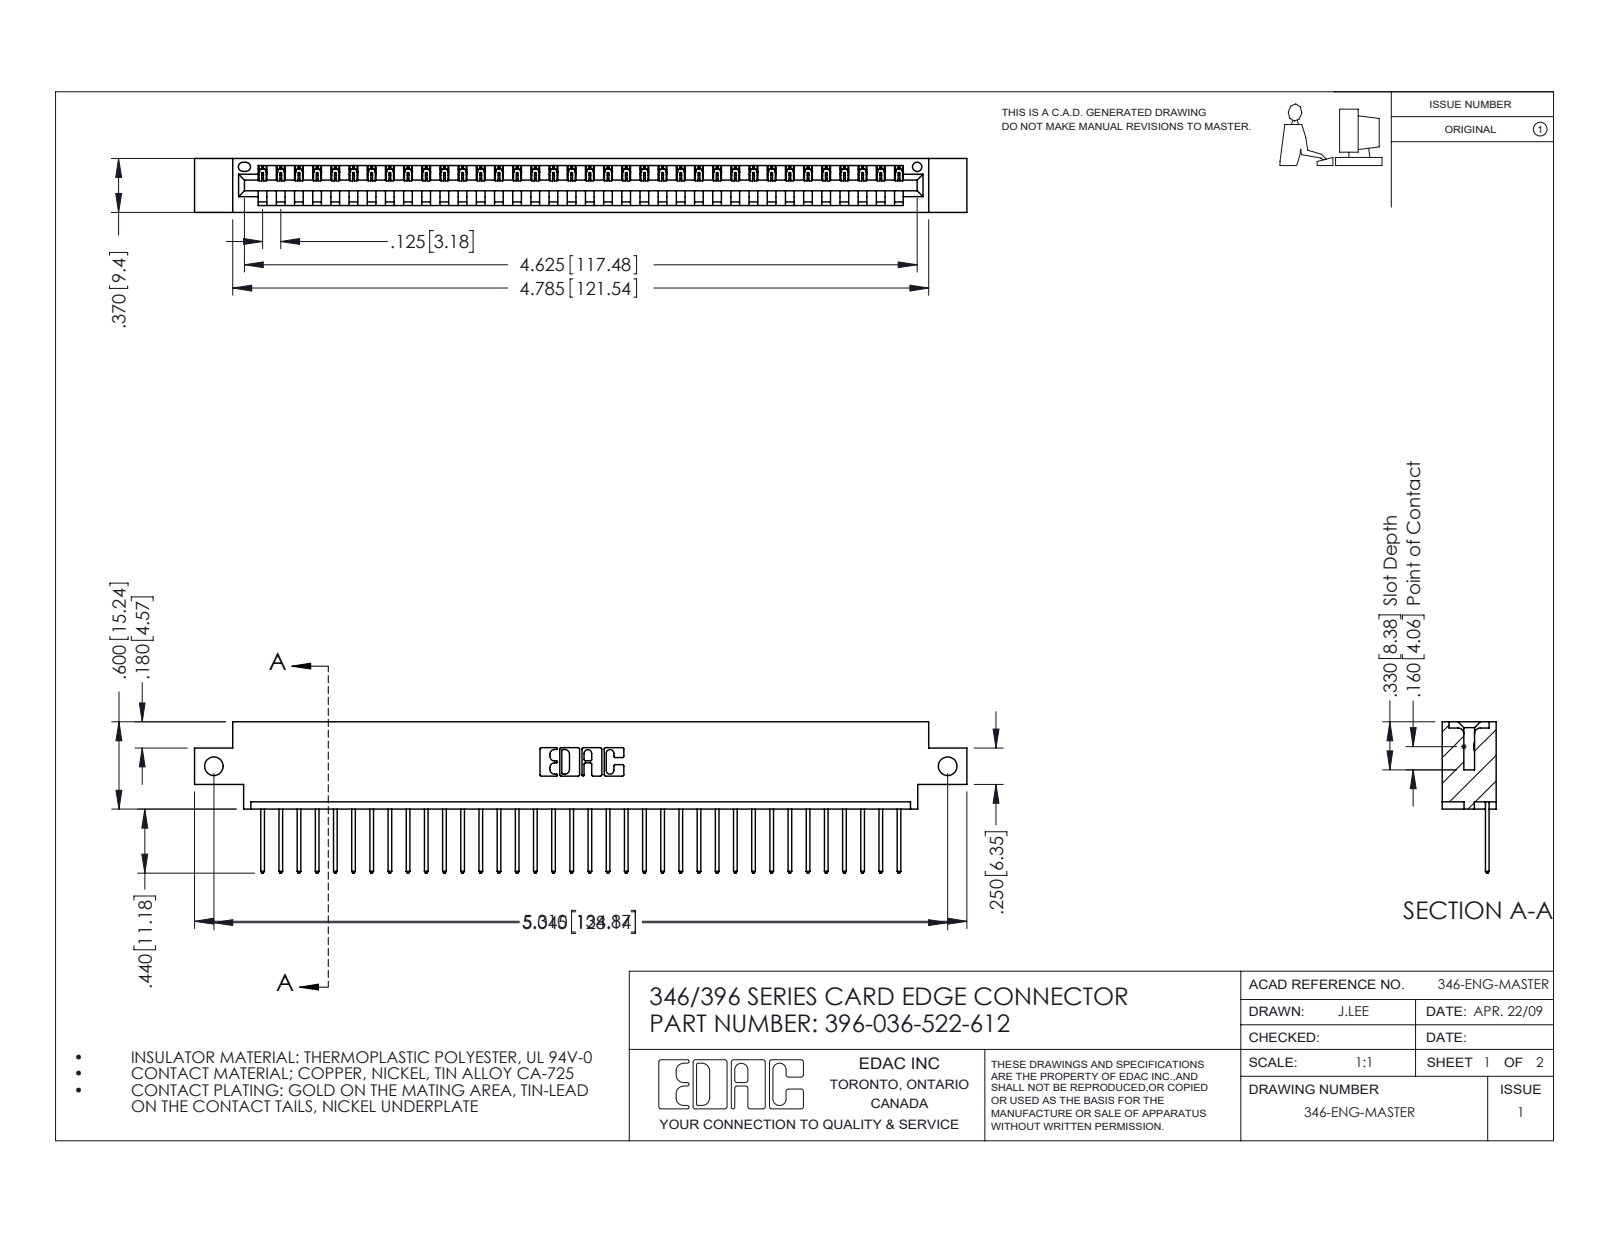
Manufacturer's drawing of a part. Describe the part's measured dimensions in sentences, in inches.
The part is named "396-036-522-612; 346 Part_0.170 Offset - Side Mount; 345-292-001_345-293-122". Its 3-D file was written by "SolidWorks 2016 (CONFIG_CONTROL_DESIGN)". It is 37 solids with 2214 faces: 1520 planar, 694 cylindrical and 0 other. Overall it measures 5.31 by 1.04 by 0.37 inches. Its volume is 0.771 cubic inches and its surface area 24.6 square inches. Round holes: 2 of diameter 0.128, 1 of diameter 0.064. Partial cylindrical surfaces (rounded edges, fillets, slot ends): 72 of radius 0.006, 72 of radius 0.01, 22 of radius 0.01, 6 of radius 0.007, 6 of radius 0.031, 3 of radius 0.026, 2 of radius 0.031, 2 of radius 0.04. The main face-to-face distances are 0.048, 0.322, 0.37, 0.25, 0.072, 0.298, 0.025, 0.148, 0.222, 0.1. The hole center spacings are 5.045.
